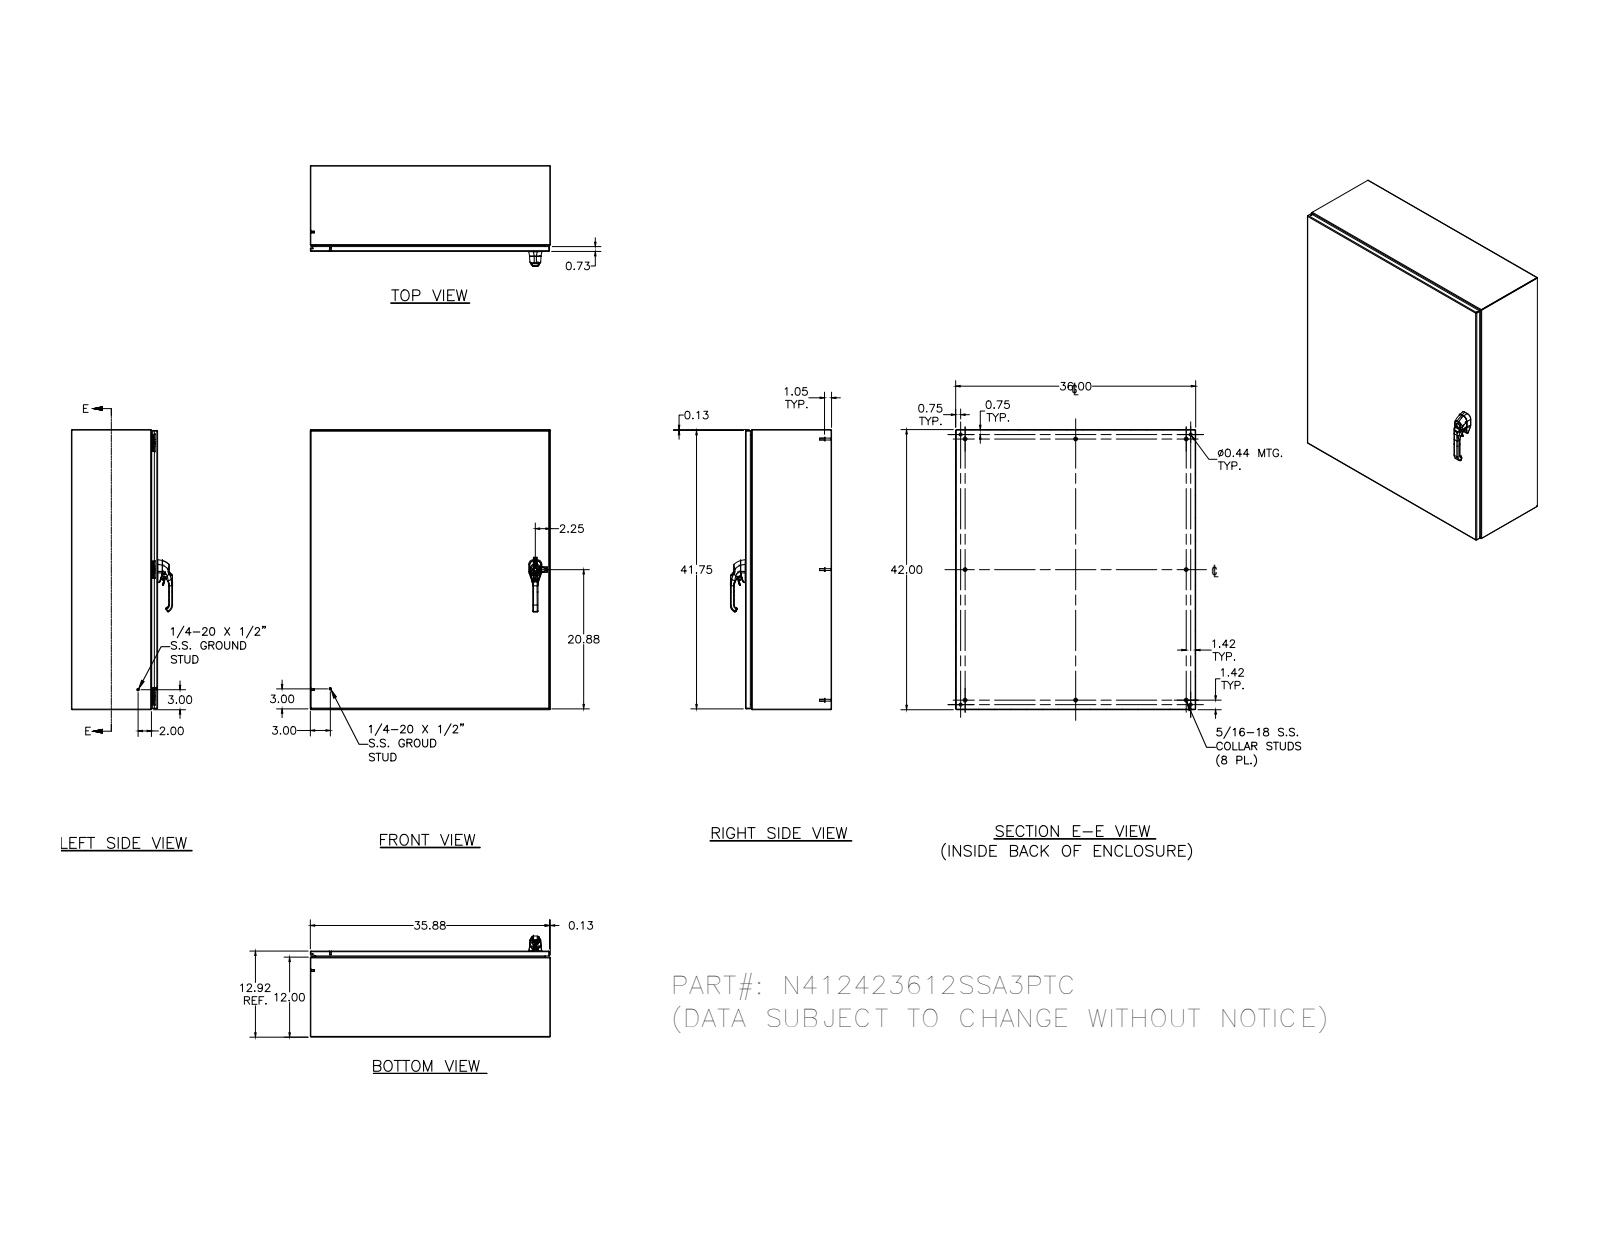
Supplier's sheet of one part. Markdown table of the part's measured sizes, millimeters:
| quantity | value |
| --- | --- |
| part name | N412423612SSA3PTC; N412423612SSA3PTCBTB; N4124212SSA3PTCLS; N4124212SSA3PTCRS (+8 more) |
| STEP written by | Autodesk Inventor 2011 (AUTOMOTIVE_DESIGN) |
| units | millimeters |
| bodies | 78 solids, 3552 faces (1203 planar, 1299 cylindrical, 1050 other) |
| overall size | 1066.8 × 914.4 × 385.2 |
| volume | 6 502 000 mm³ |
| surface area | 6 844 000 mm² |
| round holes (diameter × count) | 2.4 × 6, 3.9 × 6, 4.2 × 6, 4.4 × 6, 4.7 × 6, 4.2 × 5, 5 × 4, 11.1 × 4, 4 × 3, 5.4 × 3, 2.7 × 2, 4.1 × 2 |
| round bosses / shafts (diameter × count) | 6.4 × 14, 14.3 × 8, 7.6 × 8, 7 × 8, 9.1 × 6, 8.1 × 6, 6.5 × 6, 6 × 6 |
| partial cylindrical surfaces (radius × count) | 0.5 × 186, 0.3 × 100, 1.3 × 38, 0.8 × 32, 0.4 × 26, 3.2 × 24, 0.5 × 23, 3 × 23 |
| main face-to-face distances | 1.9, 326.2, 324.3, 328.1, 912.5, 1064.9, 910.6, 914.4, 1063, 1066.8 |
| hole center spacings | 482.6, 965.2, 482.8, 12.7, 16.7, 16.8, 33.2, 33.3 |
